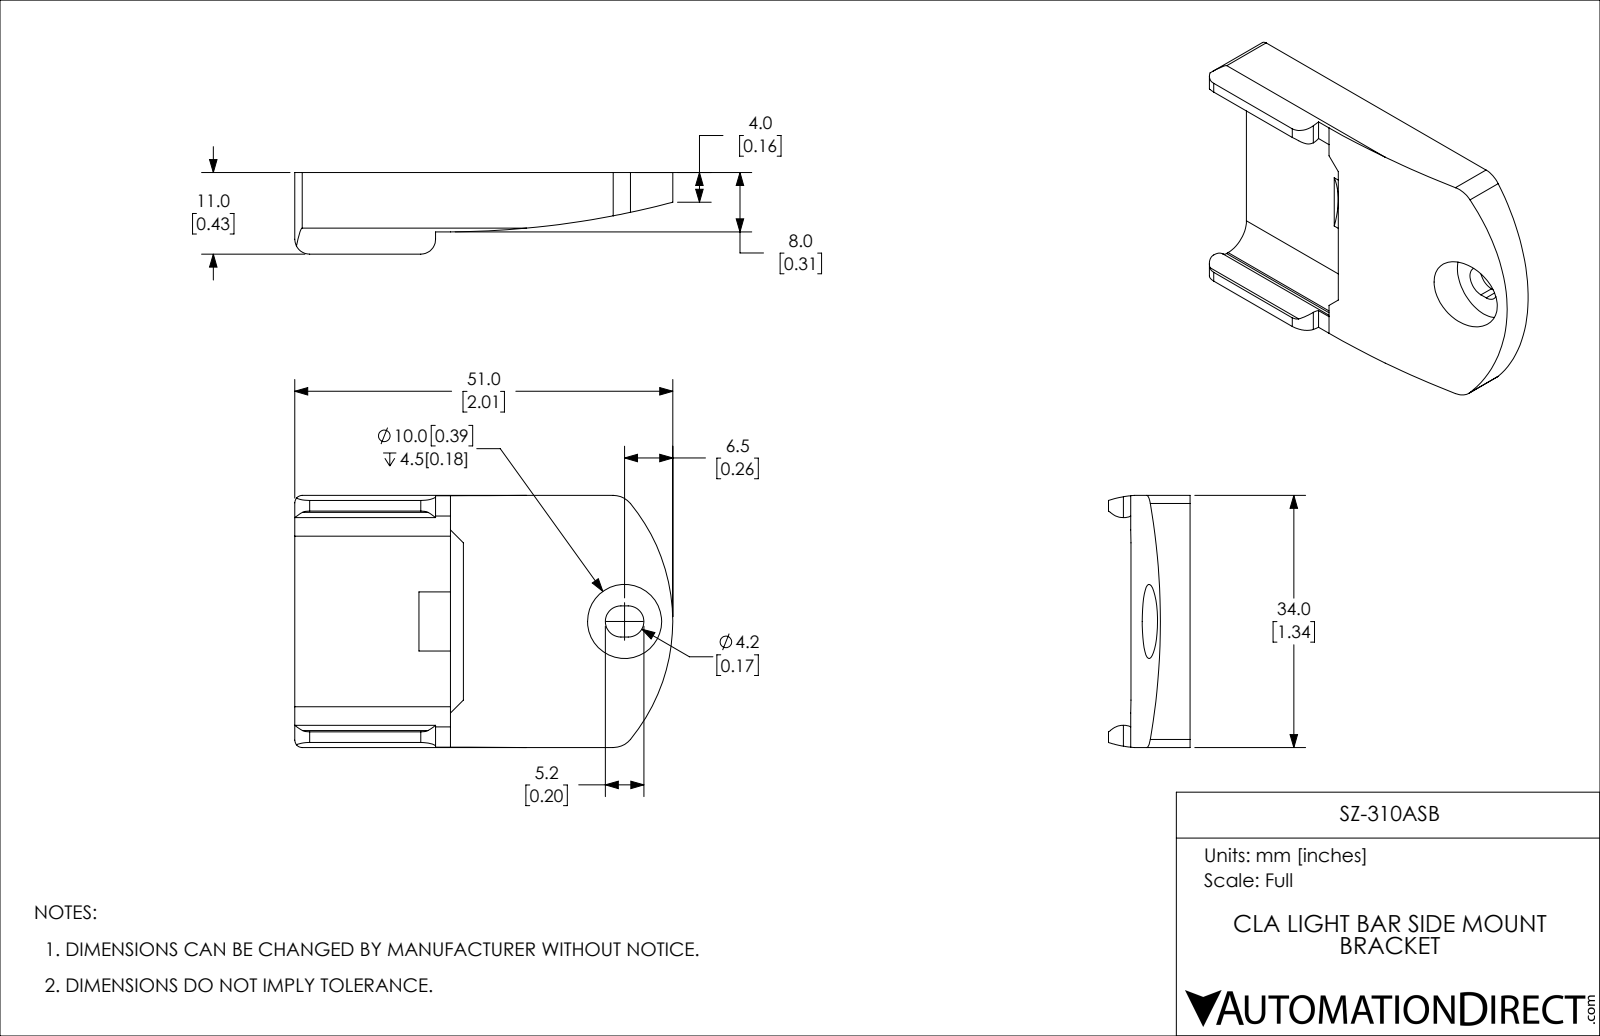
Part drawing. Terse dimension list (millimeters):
name: SZ-310ASB
written by: SolidWorks 2018 (AUTOMOTIVE_DESIGN)
unit: mm
bodies: 1 solid, 50 faces (22 planar, 28 cylindrical, 0 other)
size: 51 × 34 × 11
volume: 8 780 mm³; area: 4 941 mm²
holes: 1× ⌀10
rounds: 6× R1, 2× R2, 2× R2.1, 2× R2.5, 2× R3, 2× R3.5, 2× R15, 1× R11
face distances: 2.7, 34, 2, 22.8, 0.8, 21, 1.8, 11, 9, 8.3
